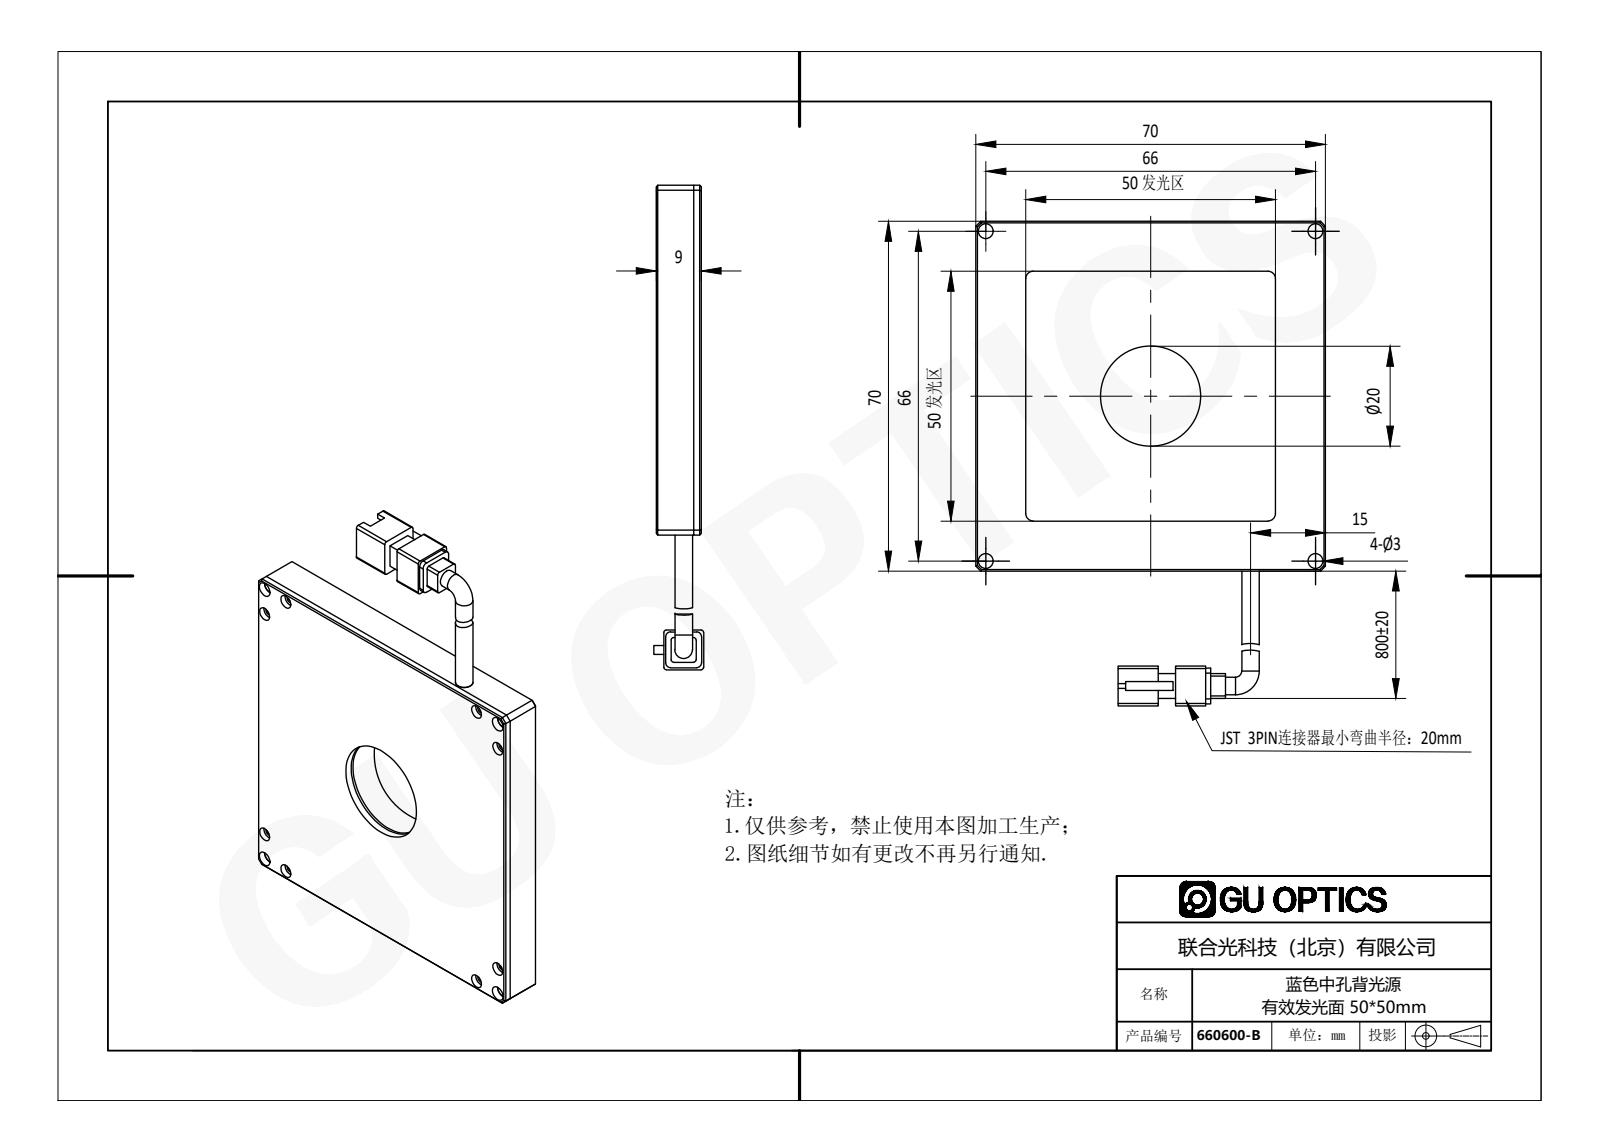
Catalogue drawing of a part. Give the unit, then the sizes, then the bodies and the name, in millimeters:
Units: millimetres
Overall size (bounding box): 97 × 70 × 10
Round holes (diameter × count): ⌀1.6 ×10, ⌀1.25 ×8, ⌀2.8 ×8, ⌀3 ×4, ⌀20 ×1
Round bosses / shafts (diameter × count): ⌀3.5 ×2
Partial cylindrical surfaces — rounded edges, fillets, slot ends (radius × count): R0.5 ×8, R2 ×6, R1 ×4, R1.5 ×4
Main face-to-face distances: 6.5, 6, 1.5, 8, 2, 1, 0.5, 3, 7, 7.5
Hole centre spacings: 66, 42.64, 60.3, 66.27, 89.2, 6, 60, 85.28
Volume: 34 282 mm³ · Surface area: 29 900 mm²
Bodies: 7 solids, 501 faces (306 planar, 118 cylindrical, 77 other)
Part name (STEP PRODUCT): 660600-B
STEP written by: SolidWorks 2016 (AUTOMOTIVE_DESIGN)
